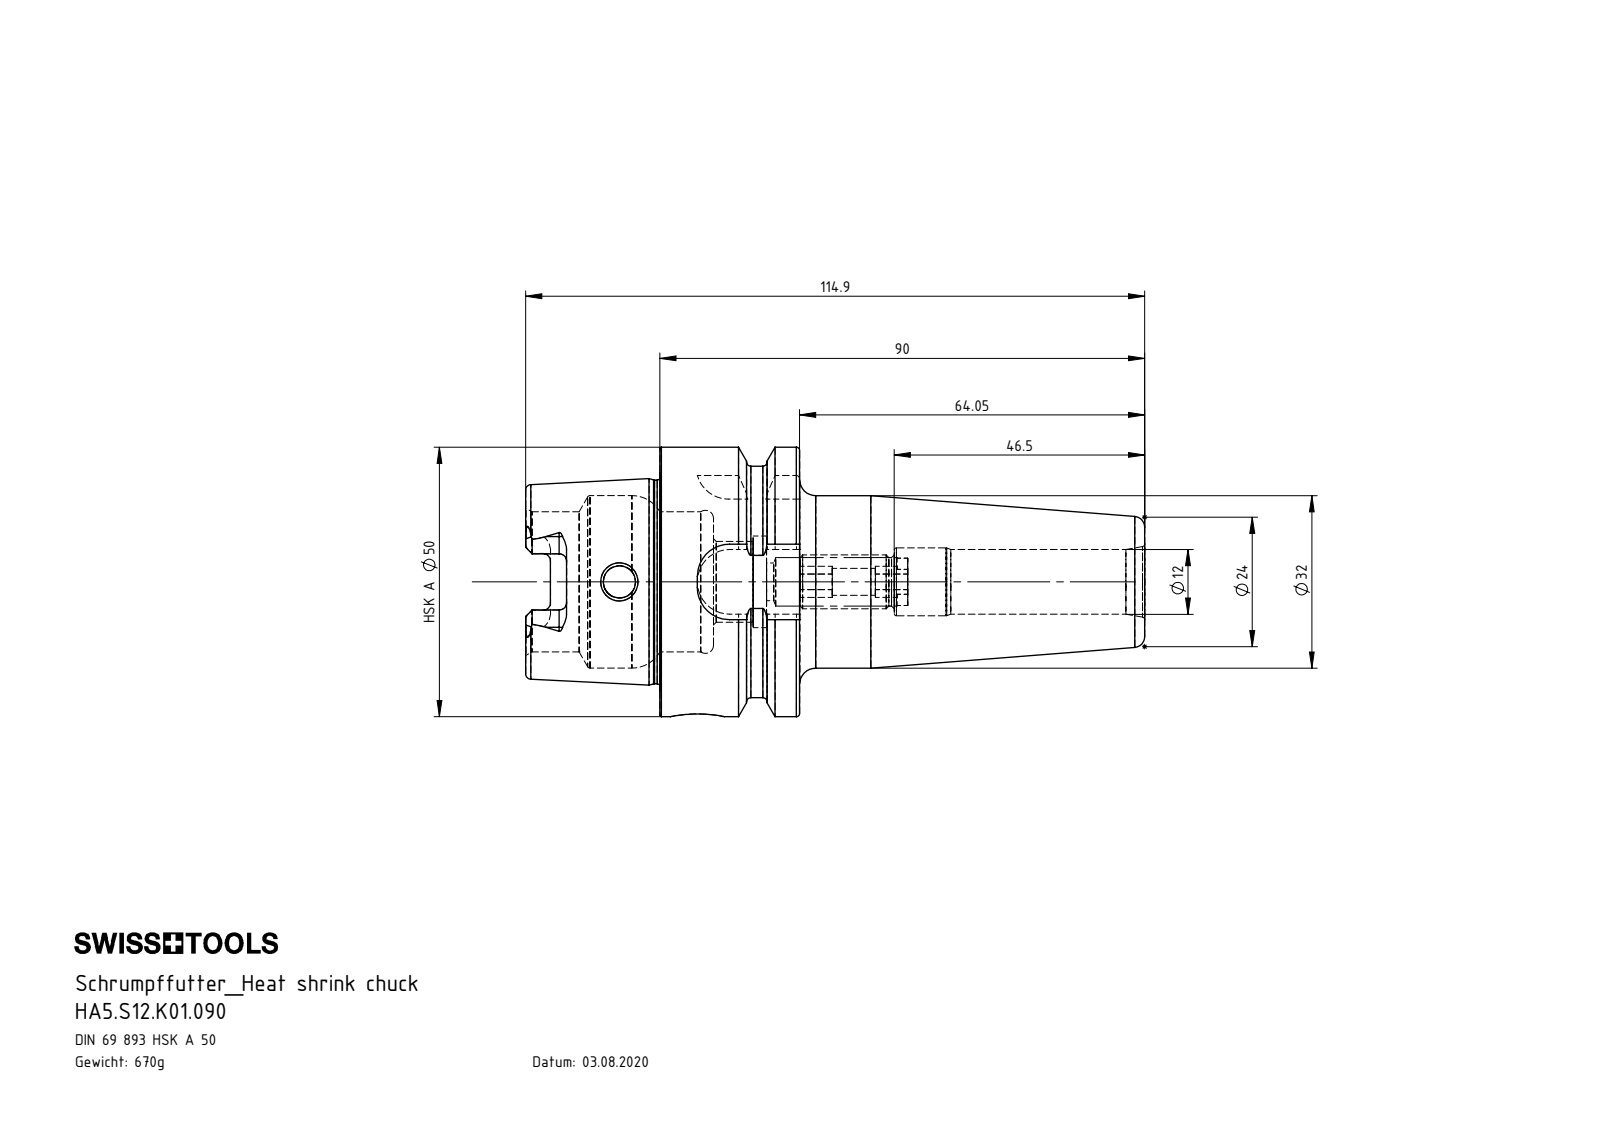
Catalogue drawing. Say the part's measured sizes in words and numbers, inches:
The part is named "HA5.S12.K01.090; HA5-S12.K01.090_A_Fertigbearbeitung; ERU-AN4.K01.020_A". Its 3-D file was written by "SolidWorks 2022 (CONFIG_CONTROL_DESIGN)". It is 2 solids with 227 faces: 80 planar, 59 cylindrical and 88 other. Overall it measures 4.524 by 1.969 by 1.969 inches. Its volume is 5.212 cubic inches and its surface area 36.74 square inches. Round holes: 1 of diameter 0.197, 1 of diameter 0.236, 1 of diameter 0.276, 1 of diameter 0.354, 1 of diameter 0.394, 1 of diameter 0.472, 1 of diameter 0.496, 1 of diameter 0.591, 1 of diameter 0.669, 1 of diameter 1.024, 1 of diameter 1.26. Round bosses or shafts: 1 of diameter 1.969, 1 of diameter 1.691, 1 of diameter 1.489, 1 of diameter 0.394. Partial cylindrical surfaces (rounded edges, fillets, slot ends): 6 of radius 0.055, 4 of radius 0.094, 4 of radius 0.236. The main face-to-face distances are 1.022, 0.392, 0.63, 0.98, 1.372, 2.002, 1.646, 1.76, 0.78, 0.388.
